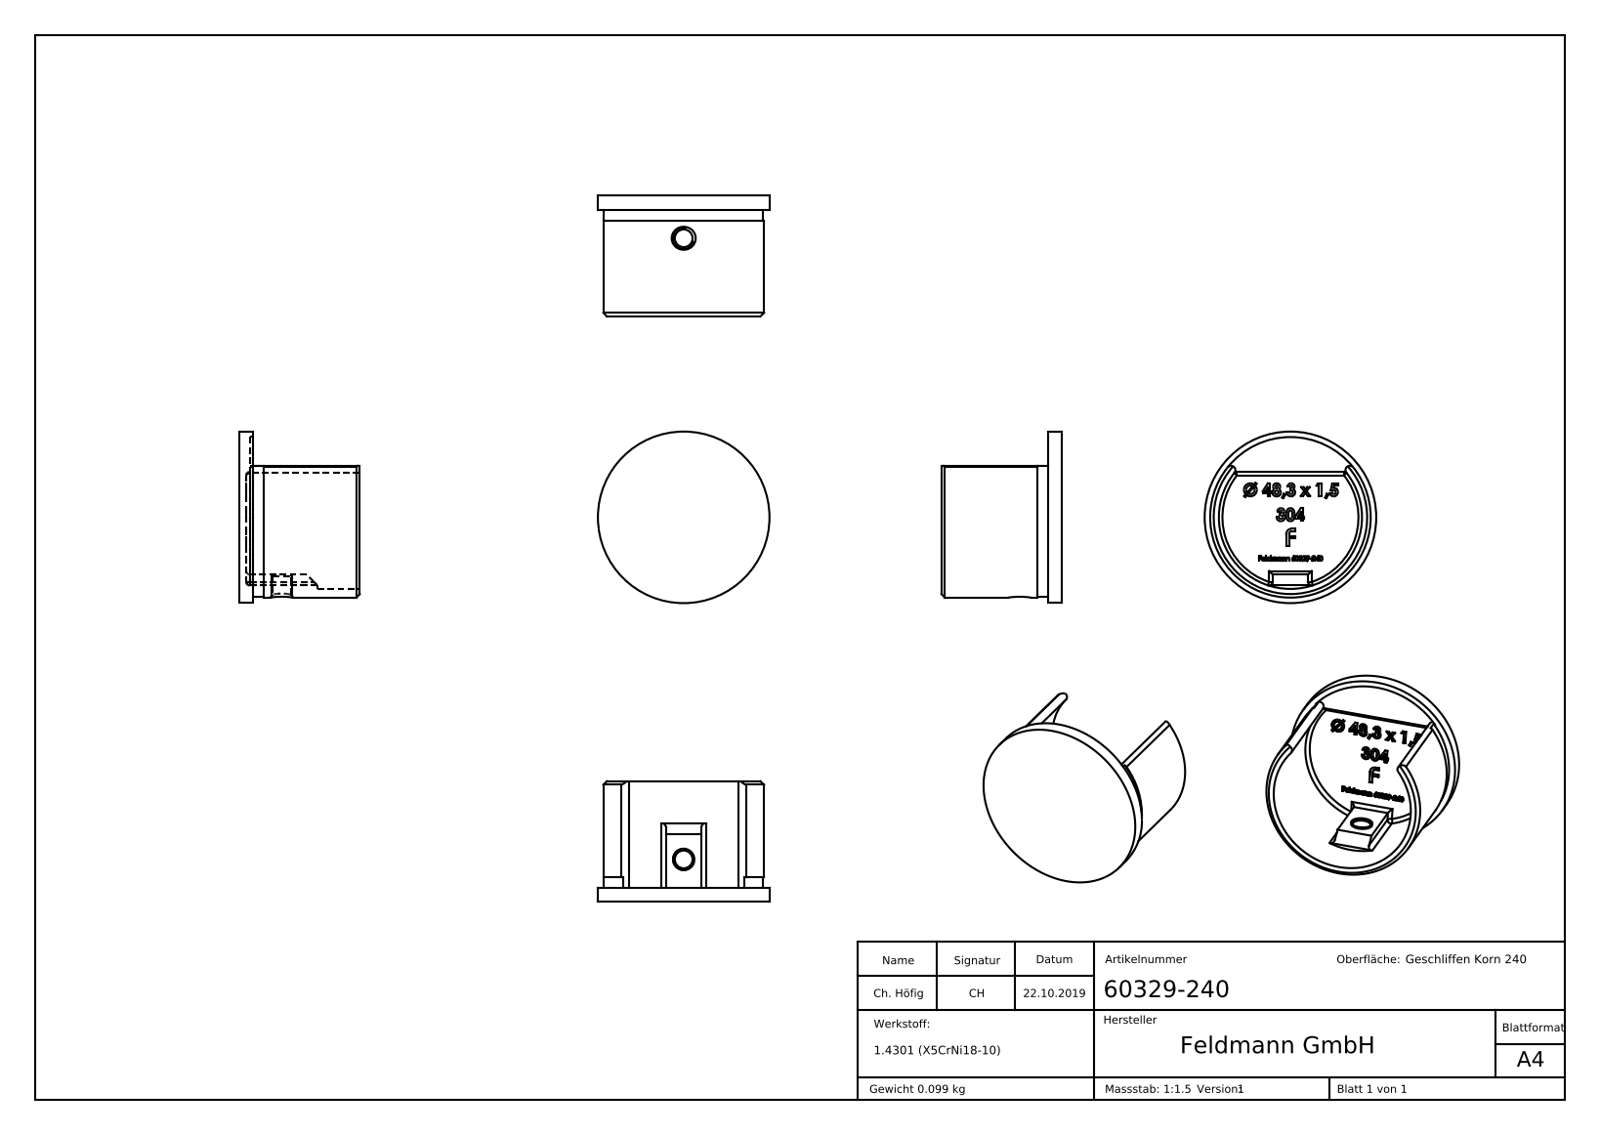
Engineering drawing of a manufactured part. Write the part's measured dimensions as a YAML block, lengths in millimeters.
part_name: "60329-240"
step_written_by: "SolidWorks 2015 (CONFIG_CONTROL_DESIGN)"
units: millimeters
bodies: {solids: 1, faces: 440, planar: 233, cylindrical: 14, other: 193}
overall_size: [48.3, 48.3, 34]
volume: 12366
surface_area: 10565
round_holes:
  - {diameter: 5, count: 1}
  - {diameter: 45.2, count: 1}
round_bosses_or_shafts:
  - {diameter: 48.3, count: 1}
partial_cylinders:
  - {radius: 1, count: 6}
  - {radius: 1.23, count: 2}
  - {radius: 20.15, count: 1}
  - {radius: 22.4, count: 1}
face_to_face_distances: [2, 1, 4, 3, 30, 31, 32, 34, 1.9, 2.1]
